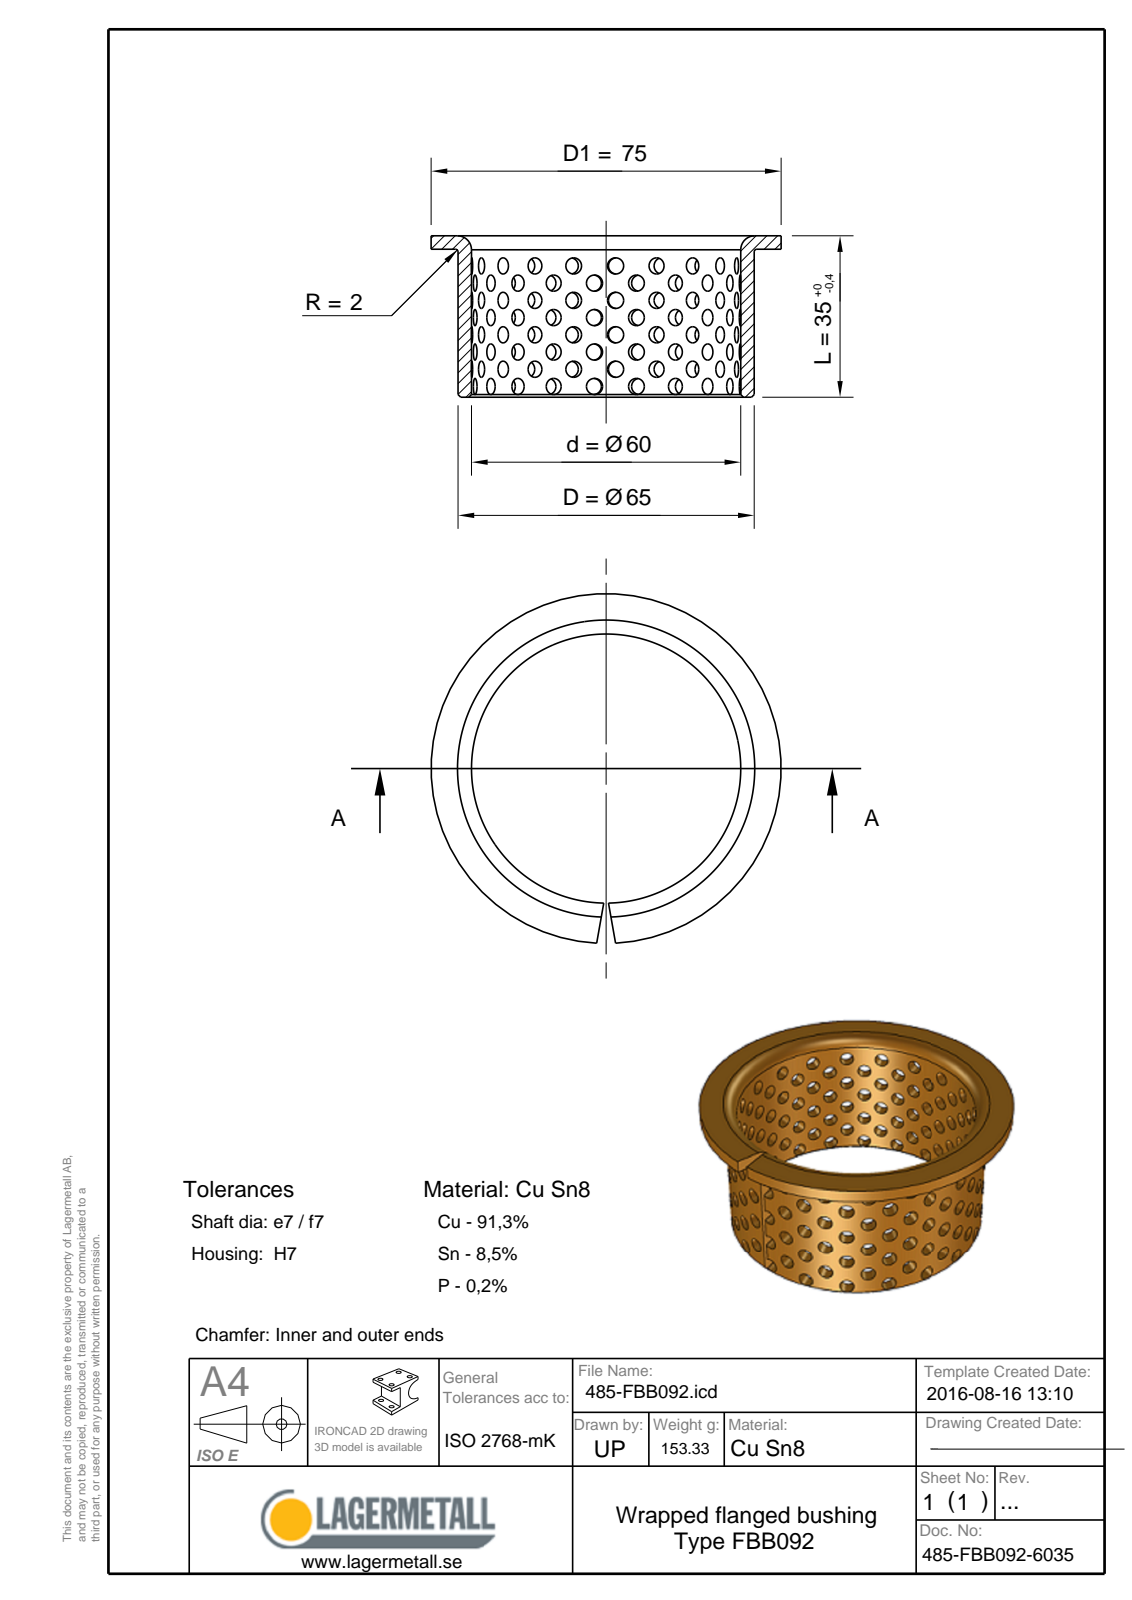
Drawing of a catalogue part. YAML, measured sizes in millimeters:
part_name: "485-FBB092-6035"
step_written_by: "Spatial InterOp 3D (CONFIG_CONTROL_DESIGN)"
units: millimeters
bodies: {solids: 1, faces: 12, planar: 5, cylindrical: 3, other: 4}
overall_size: [75, 74.96, 35]
volume: 18930
surface_area: 16341
round_holes:
  - {diameter: 60, count: 1}
round_bosses_or_shafts:
  - {diameter: 75, count: 1}
  - {diameter: 65, count: 1}
face_to_face_distances: [2.5, 32.5, 35]
